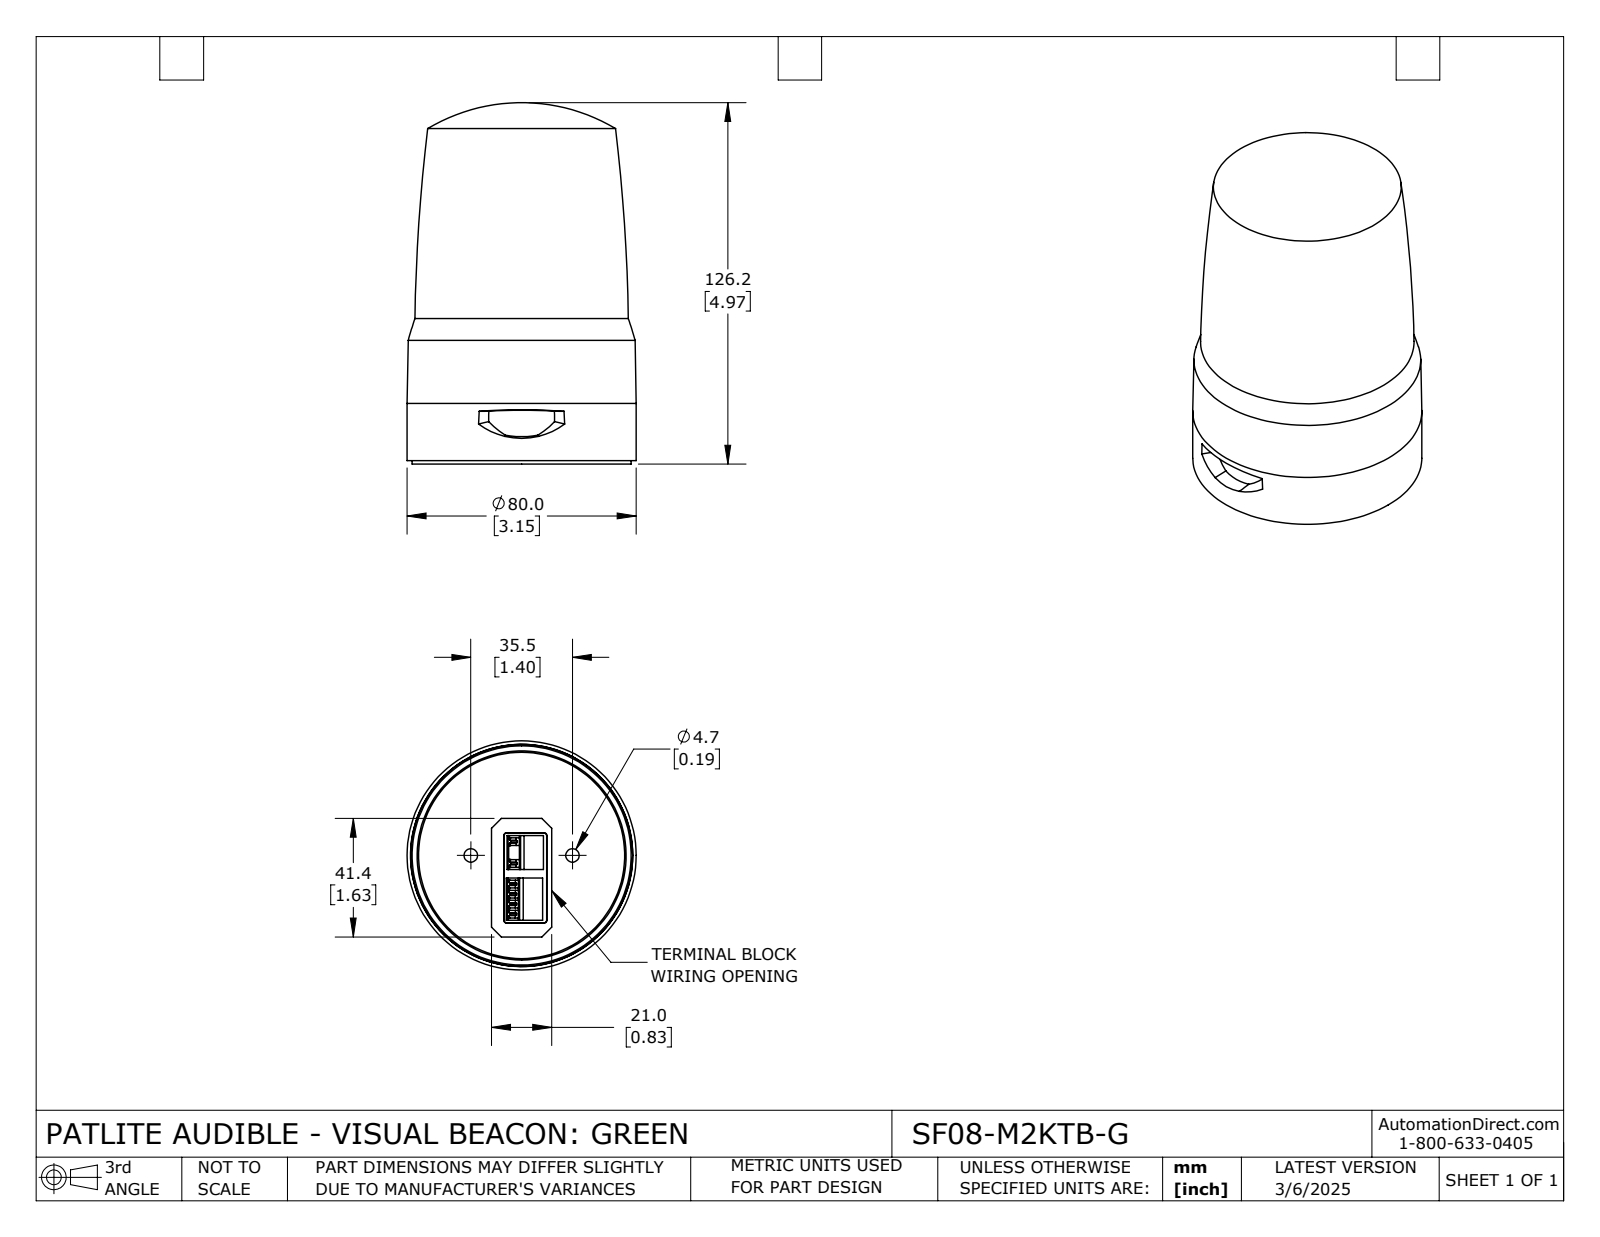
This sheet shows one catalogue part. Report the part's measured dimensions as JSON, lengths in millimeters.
{"part_name": "SF08-M2KTB-G", "step_written_by": "SolidWorks 2024 (CONFIG_CONTROL_DESIGN)", "units": "millimeters", "bodies": {"solids": 2, "faces": 262, "planar": 168, "cylindrical": 32, "other": 62}, "overall_size": [126.2, 80, 80], "volume_mm3": 488153, "surface_area_mm2": 54584, "round_holes": [[4.7, 2], [12.2, 2], [73, 1]], "round_bosses_or_shafts": [[80, 1], [76.5, 1], [74.6, 1], [72, 1]], "partial_cylinders_radius": [[1, 4], [0.3, 2], [34.6, 1], [35, 1]], "face_to_face_distances": [15.7, 6.3, 9.4, 3, 5.1, 14.5, 3.15, 6.15, 1.3, 12.45], "hole_center_spacings": [17.75, 35.5]}
